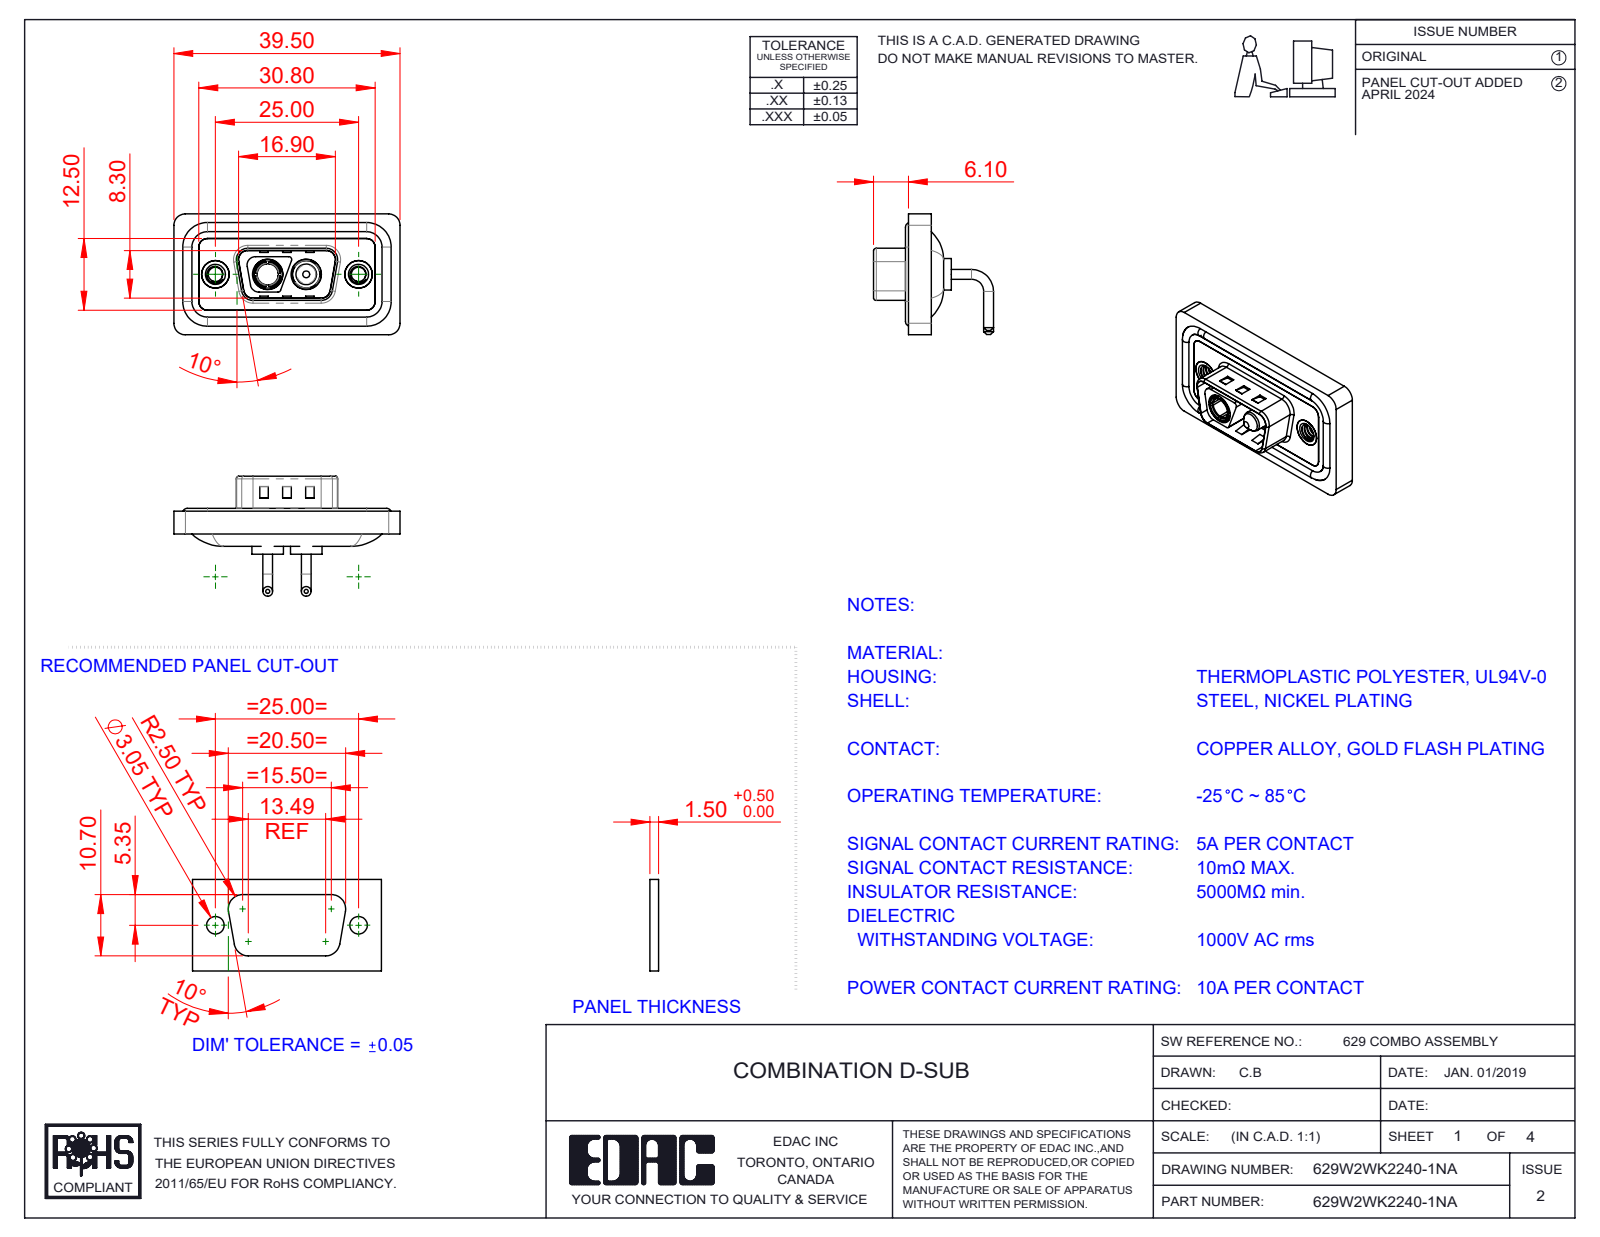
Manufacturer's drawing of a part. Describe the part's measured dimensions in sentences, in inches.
The part is named "629Combo Waterproof Housing_09 Contacts; 629Combo Shell Rear_09 Contacts; Power Pin_10A RA; 629Combo Threaded Rivet_A (+4 more)". Its 3-D file was written by "SolidWorks 2023 (CONFIG_CONTROL_DESIGN)". It is 11 solids with 536 faces: 189 planar, 229 cylindrical and 118 other. Overall it measures 1.555 by 0.831 by 0.825 inches. Its volume is 0.279 cubic inches and its surface area 11.52 square inches. Round holes: 2 of diameter 0.098, 2 of diameter 0.157, 2 of diameter 0.189, 2 of diameter 0.191, 2 of diameter 0.197, 2 of diameter 0.209, 1 of diameter 0.146. Round bosses or shafts: 4 of diameter 0.067, 4 of diameter 0.063, 2 of diameter 0.217, 2 of diameter 0.205, 2 of diameter 0.193, 2 of diameter 0.187, 2 of diameter 0.148, 1 of diameter 0.195. Partial cylindrical surfaces (rounded edges, fillets, slot ends): 20 of radius 0.059, 18 of radius 0.079, 10 of radius 0.02, 8 of radius 0.063, 4 of radius 0.01, 4 of radius 0.024, 4 of radius 0.026, 4 of radius 0.035. The main face-to-face distances are 0.016, 0.114, 0.043, 0.031, 0.083, 0.098, 0.122, 0.063, 0.177, 0.059. The hole center spacings are 0.36, 0.624, 0.265, 0.984.
